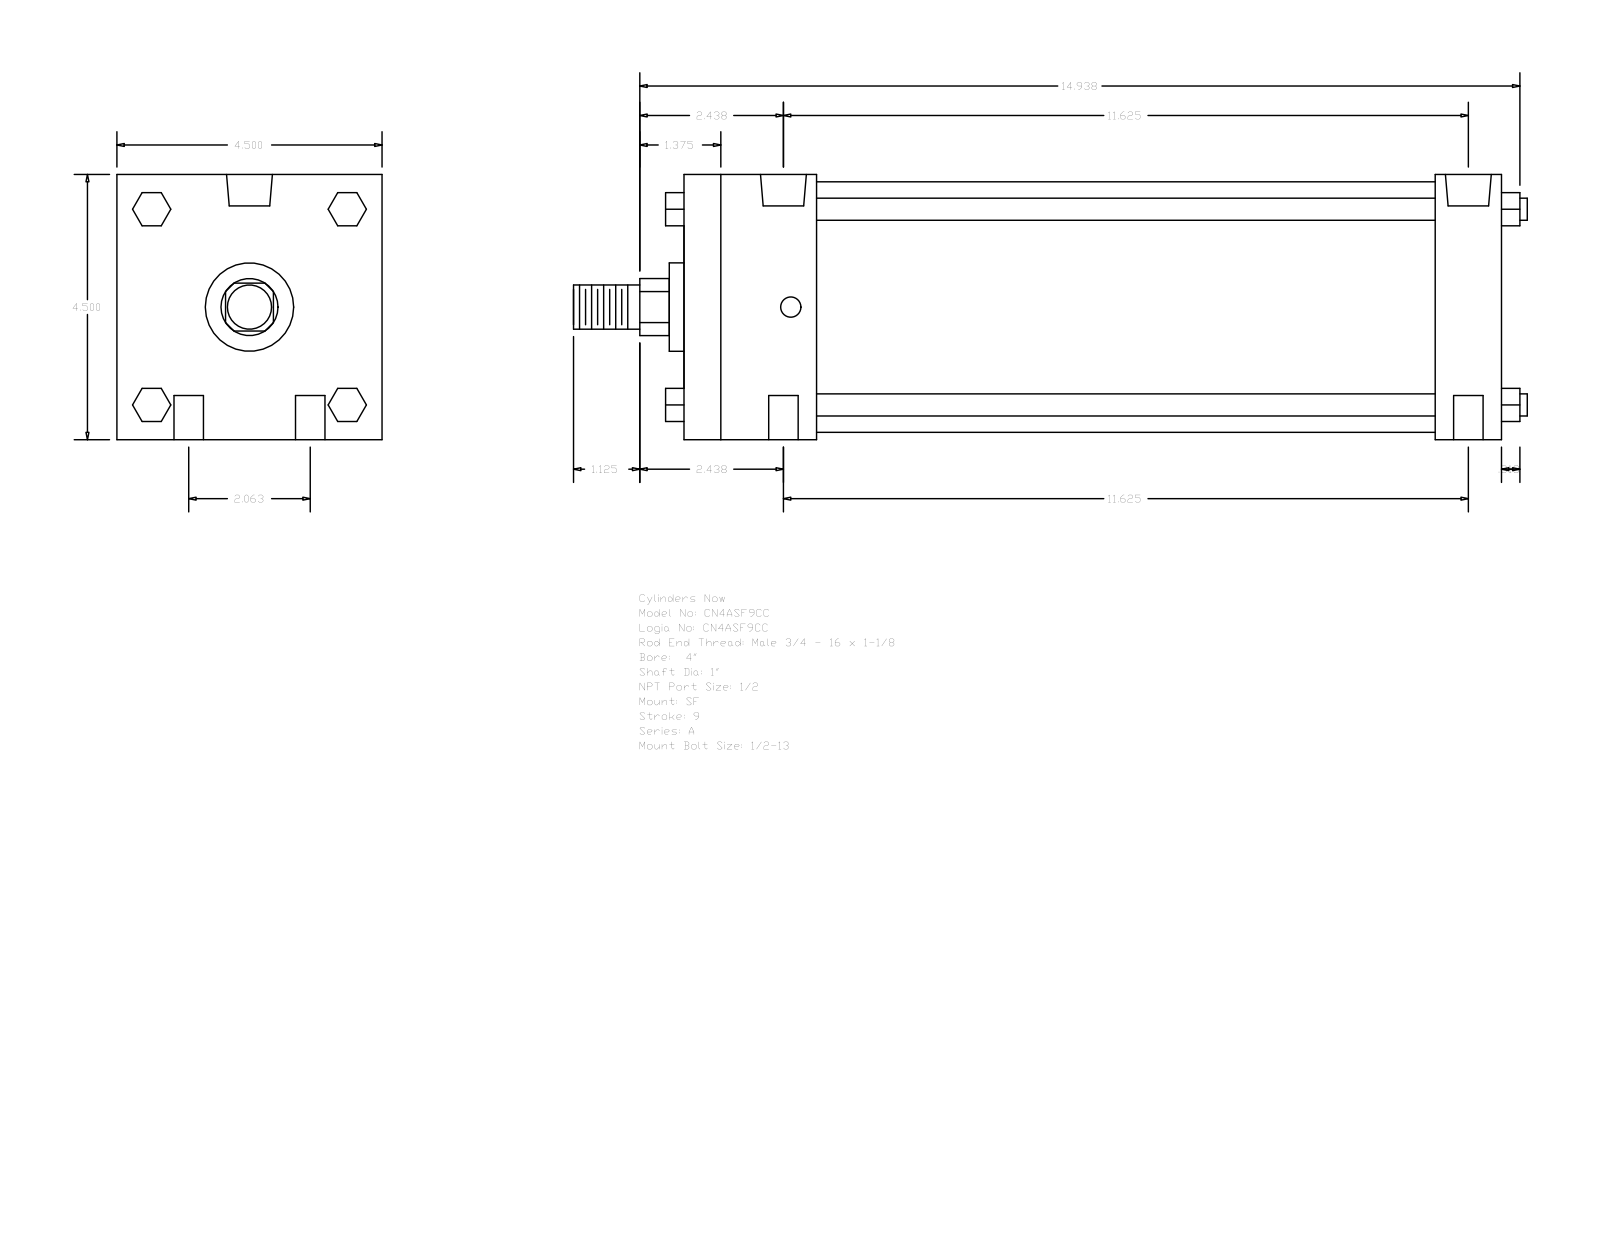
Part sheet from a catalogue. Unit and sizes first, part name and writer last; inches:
Units: inches
Overall size (bounding box): 16.187 × 4.5 × 4.5
Round holes (diameter × count): ⌀0.5 ×4, ⌀0.344 ×2, ⌀0.778 ×2
Round bosses / shafts (diameter × count): ⌀0.375 ×4, ⌀4.25 ×1, ⌀1.5 ×1, ⌀1 ×1, ⌀0.75 ×1
Partial cylindrical surfaces — rounded edges, fillets, slot ends (radius × count): R0.484 ×1
Main face-to-face distances: 4.5, 13.875, 12.75, 1.125, 2.25, 10.5, 11.625, 0.563, 1.66, 2.875
Hole centre spacings: 1.031, 11.671, 11.625, 2.062, 11.807, 11.375
Bodies: 0 solids, 124 faces (94 planar, 30 cylindrical, 0 other)
Part name (STEP PRODUCT): A_SF__0400_1
STEP written by: GSSL Pune (CONFIG_CONTROL_DESIGN)
